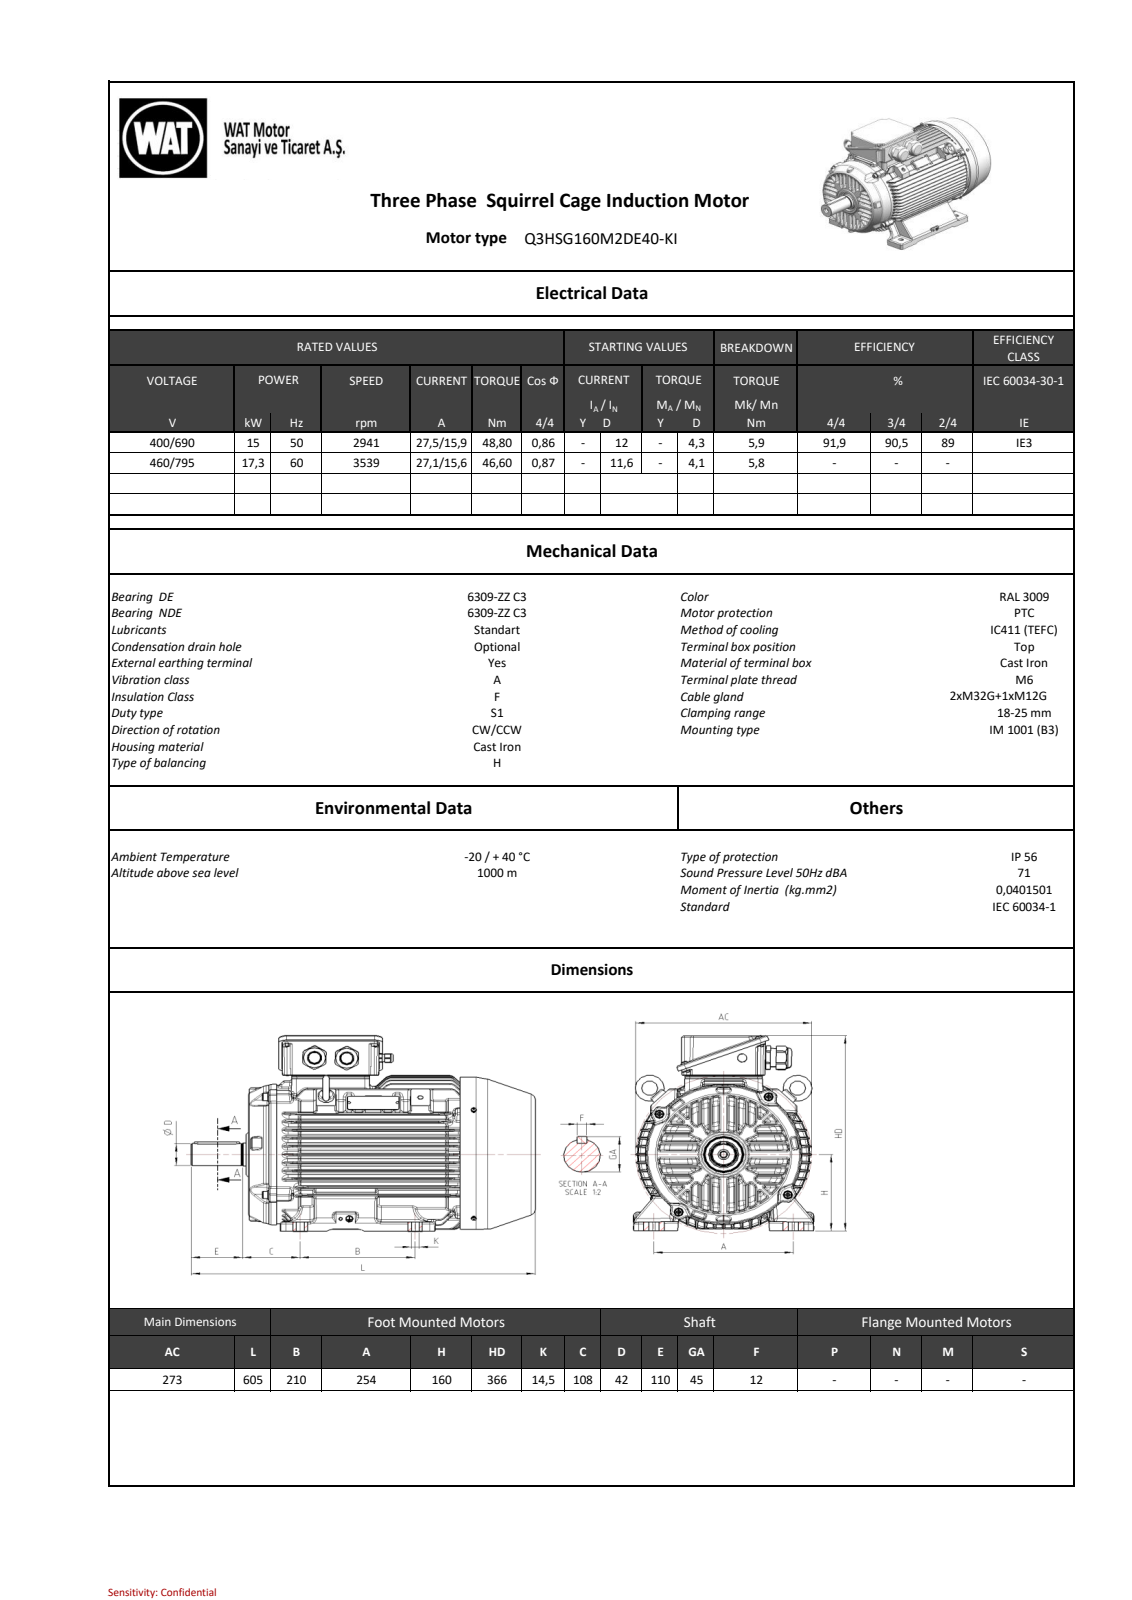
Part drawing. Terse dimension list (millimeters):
name: C9017F38B806sw2y
written by: SIEMENS PLM Software NX 11.0 (AUTOMOTIVE_DESIGN)
unit: mm
bodies: 0 solids, 6796 faces (1235 planar, 1835 cylindrical, 3726 other)
size: 605 × 365.99 × 317.6
holes: 8× ⌀6.8, 2× ⌀2.5, 2× ⌀3.2, 2× ⌀8.5, 1× ⌀4.2, 1× ⌀10.2, 1× ⌀13, 1× ⌀19, 1× ⌀21, 1× ⌀68.67, 1× ⌀180, 1× ⌀264
bosses: 4× ⌀16, 4× ⌀13, 4× ⌀10, 4× ⌀8.65, 4× ⌀8, 4× ⌀5, 2× ⌀25, 1× ⌀267
rounds: 226× R3, 212× R4.5, 106× R1.5, 72× R2, 72× R4, 60× R1.8, 55× R6, 36× R1
face distances: 13.76, 13.83, 27.59, 27.73, 13.9, 41.49, 55.44, 41.68, 27.85, 13.95
hole spacings: 121.5, 171.83, 42.2, 139.38, 199.06, 239.31, 243.01, 35.5
